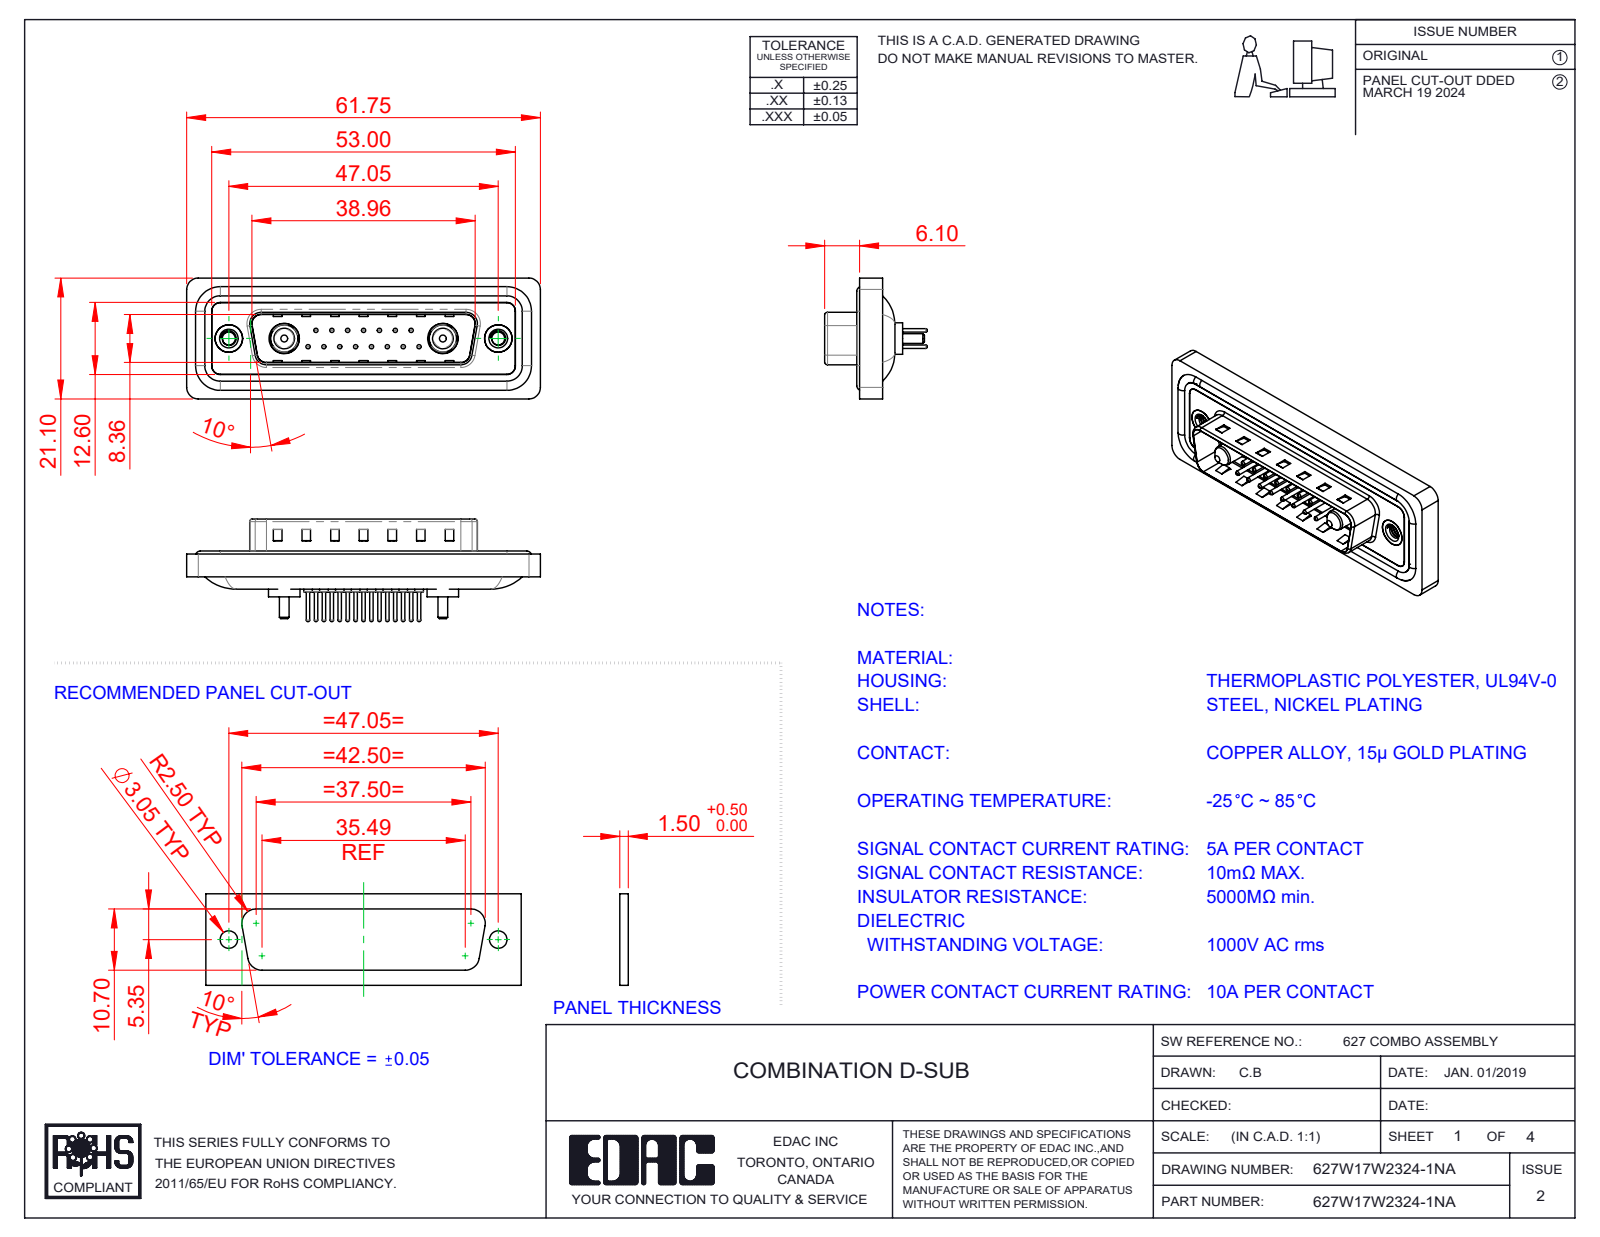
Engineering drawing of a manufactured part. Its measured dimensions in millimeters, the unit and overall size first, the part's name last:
Units: millimetres
Overall size (bounding box): 61.75 × 21.1 × 17.9
Round holes (diameter × count): ⌀0.75 ×15, ⌀1.6 ×15, ⌀2 ×15, ⌀2.26 ×2, ⌀4 ×2, ⌀4.8 ×2, ⌀4.85 ×2, ⌀5 ×2, ⌀5.3 ×2
Round bosses / shafts (diameter × count): ⌀1.5 ×15, ⌀0.6 ×15, ⌀1.6 ×4, ⌀5.5 ×2, ⌀5.2 ×2, ⌀4.9 ×2, ⌀4.75 ×2, ⌀3.75 ×2
Partial cylindrical surfaces — rounded edges, fillets, slot ends (radius × count): R1.5 ×22, R2 ×18, R0.5 ×8, R1.6 ×8, R0.25 ×4, R0.6 ×4, R0.65 ×4, R0.9 ×4
Main face-to-face distances: 0.4, 1.5, 1.1, 1.6, 0.5, 3.1, 2.9, 0.82, 9.58, 4.1
Hole centre spacings: 3.16, 2.77, 5.54, 8.31, 5.04, 7.49, 11.08, 5.03
Volume: 7 239 mm³ · Surface area: 11 886 mm²
Bodies: 26 solids, 1114 faces (334 planar, 438 cylindrical, 342 other)
Part name (STEP PRODUCT): Power Pin_10A S; 627W17W2324-1NA; 627Combo Shell Front_25 Contacts; 627Combo Contact Row 1_24 (+5 more)
STEP written by: SolidWorks 2023 (CONFIG_CONTROL_DESIGN)
